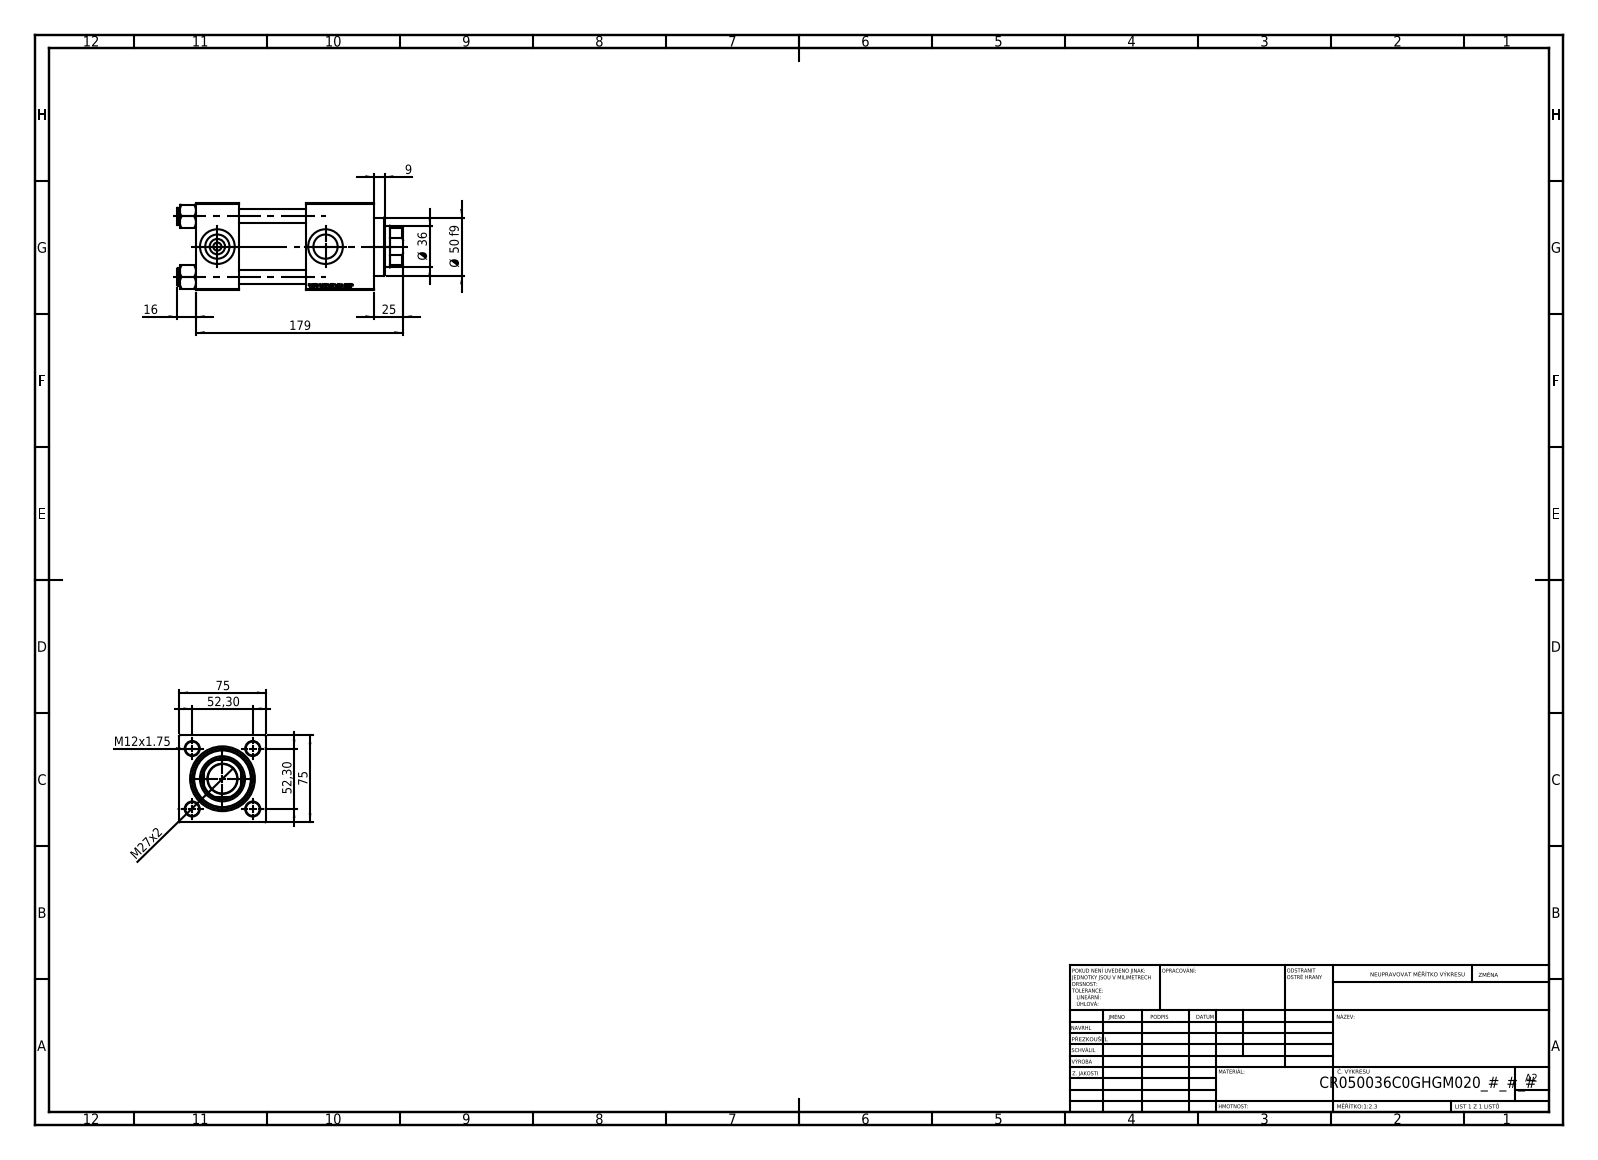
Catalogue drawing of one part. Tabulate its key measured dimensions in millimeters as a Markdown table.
| quantity | value |
| --- | --- |
| part name | V215CR_VCP_C; V215_VC_A; V215CR_C_Body; NUT_M5_C (+1 more) |
| STEP written by | SolidWorks 2019 (CONFIG_CONTROL_DESIGN) |
| units | millimeters |
| bodies | 11 solids, 1148 faces (526 planar, 86 cylindrical, 536 other) |
| overall size | 195 × 75.54 × 75 |
| volume | 686 044 mm³ |
| surface area | 155 490 mm² |
| round holes (diameter × count) | 12 × 4, 7 × 2, 20.96 × 2, 30 × 2, 25.5 × 1, 36 × 1, 39 × 1, 41 × 1, 53 × 1 |
| round bosses / shafts (diameter × count) | 15 × 4, 56 × 1, 50 × 1 |
| partial cylindrical surfaces (radius × count) | 17.5 × 1 |
| main face-to-face distances | 75, 37, 95, 58, 154, 117, 59, 125.3, 88.3, 30.3 |
| hole center spacings | 36.98, 52.3, 73.96, 93.5 |
